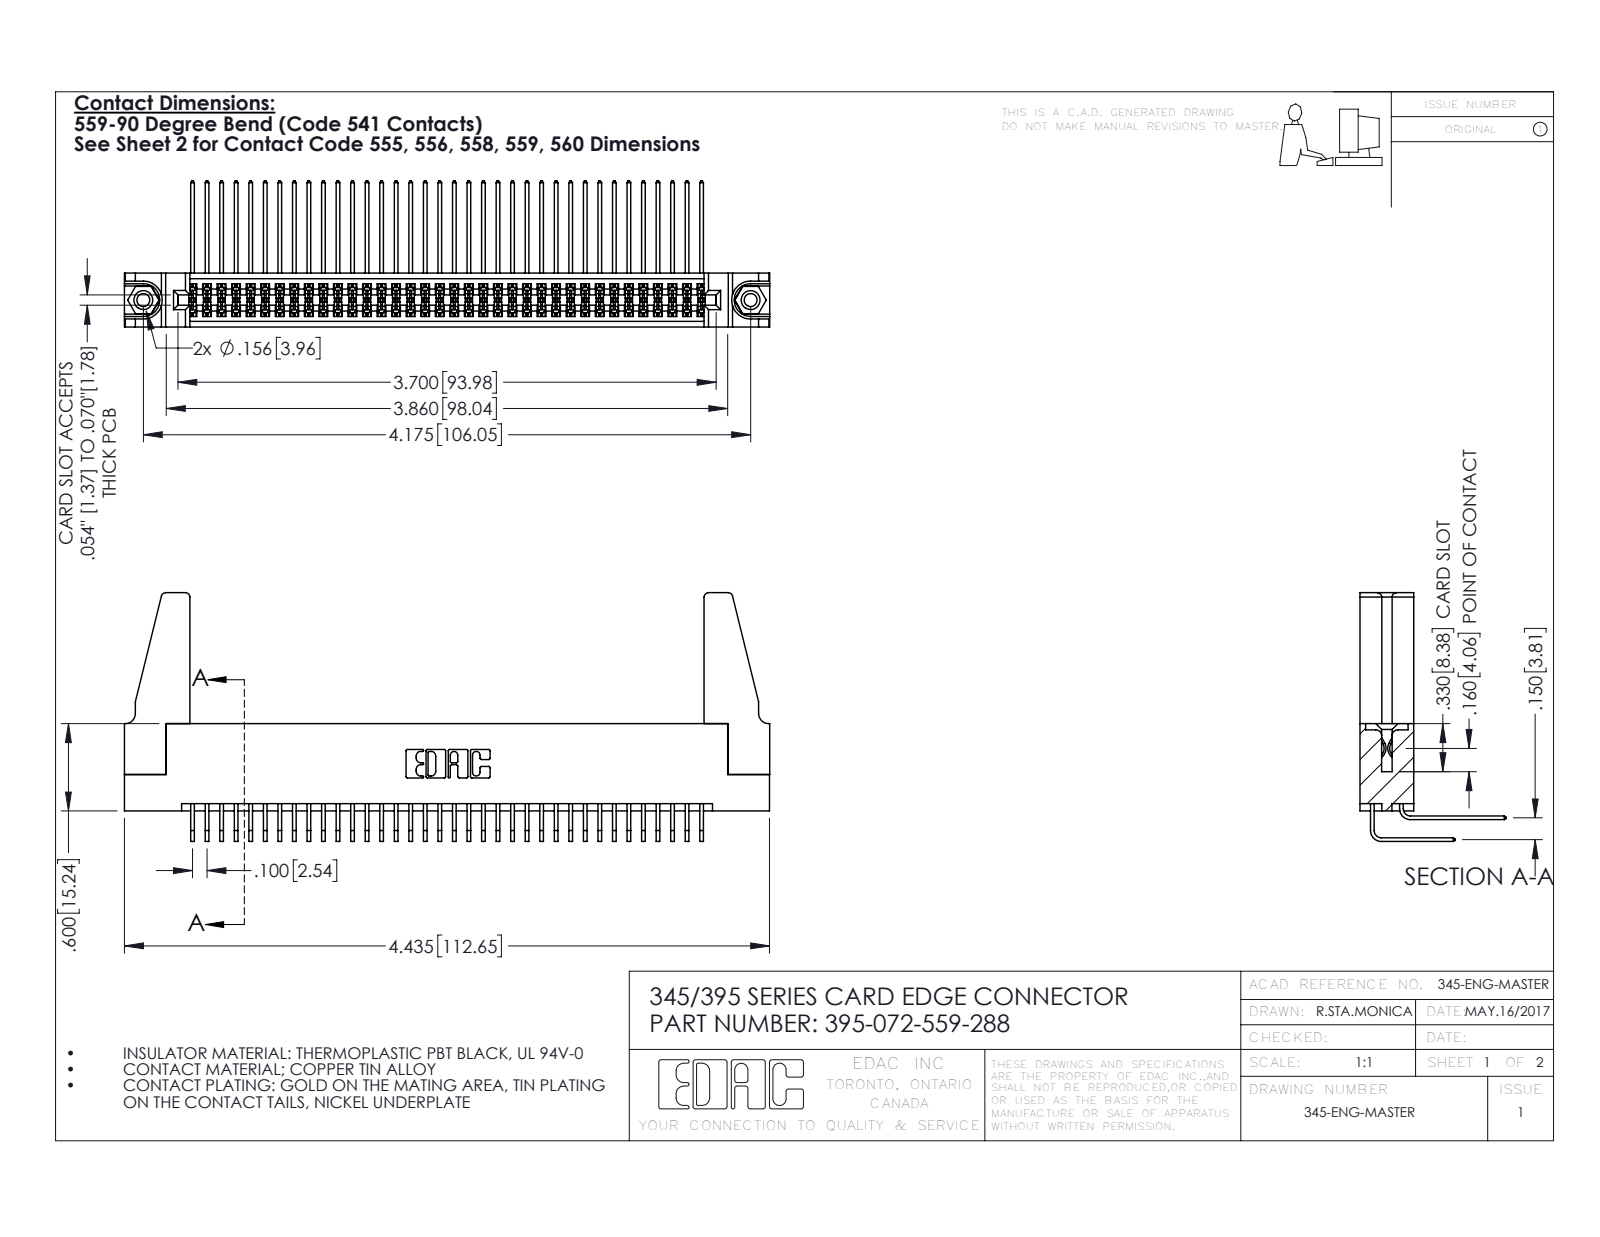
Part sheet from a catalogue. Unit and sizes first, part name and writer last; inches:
Units: inches
Overall size (bounding box): 4.436 × 1.709 × 1.005
Round holes (diameter × count): ⌀0.089 ×2, ⌀0.125 ×2, ⌀0.156 ×2, ⌀0.064 ×1
Round bosses / shafts (diameter × count): ⌀0.155 ×2
Partial cylindrical surfaces — rounded edges, fillets, slot ends (radius × count): R0.006 ×109, R0.01 ×22, R0.03 ×8, R0.007 ×6, R0.031 ×6, R0.026 ×3, R0.014 ×2, R0.019 ×2
Main face-to-face distances: 0.072, 0.298, 0.37, 0.2, 0.098, 0.272, 0.025, 0.225, 0.175, 0.15
Hole centre spacings: 0.27, 3.939, 4.175
Volume: 0.888 in³ · Surface area: 33.59 in²
Bodies: 77 solids, 3994 faces (2672 planar, 1306 cylindrical, 16 other)
Part name (STEP PRODUCT): 345-292-001_558 559 Tail - 1; 395-072-559-288; 345-250-001_345-250-001-102; 345-292-001_559 Tail - 2 (+2 more)
STEP written by: SolidWorks 2016 (CONFIG_CONTROL_DESIGN)
